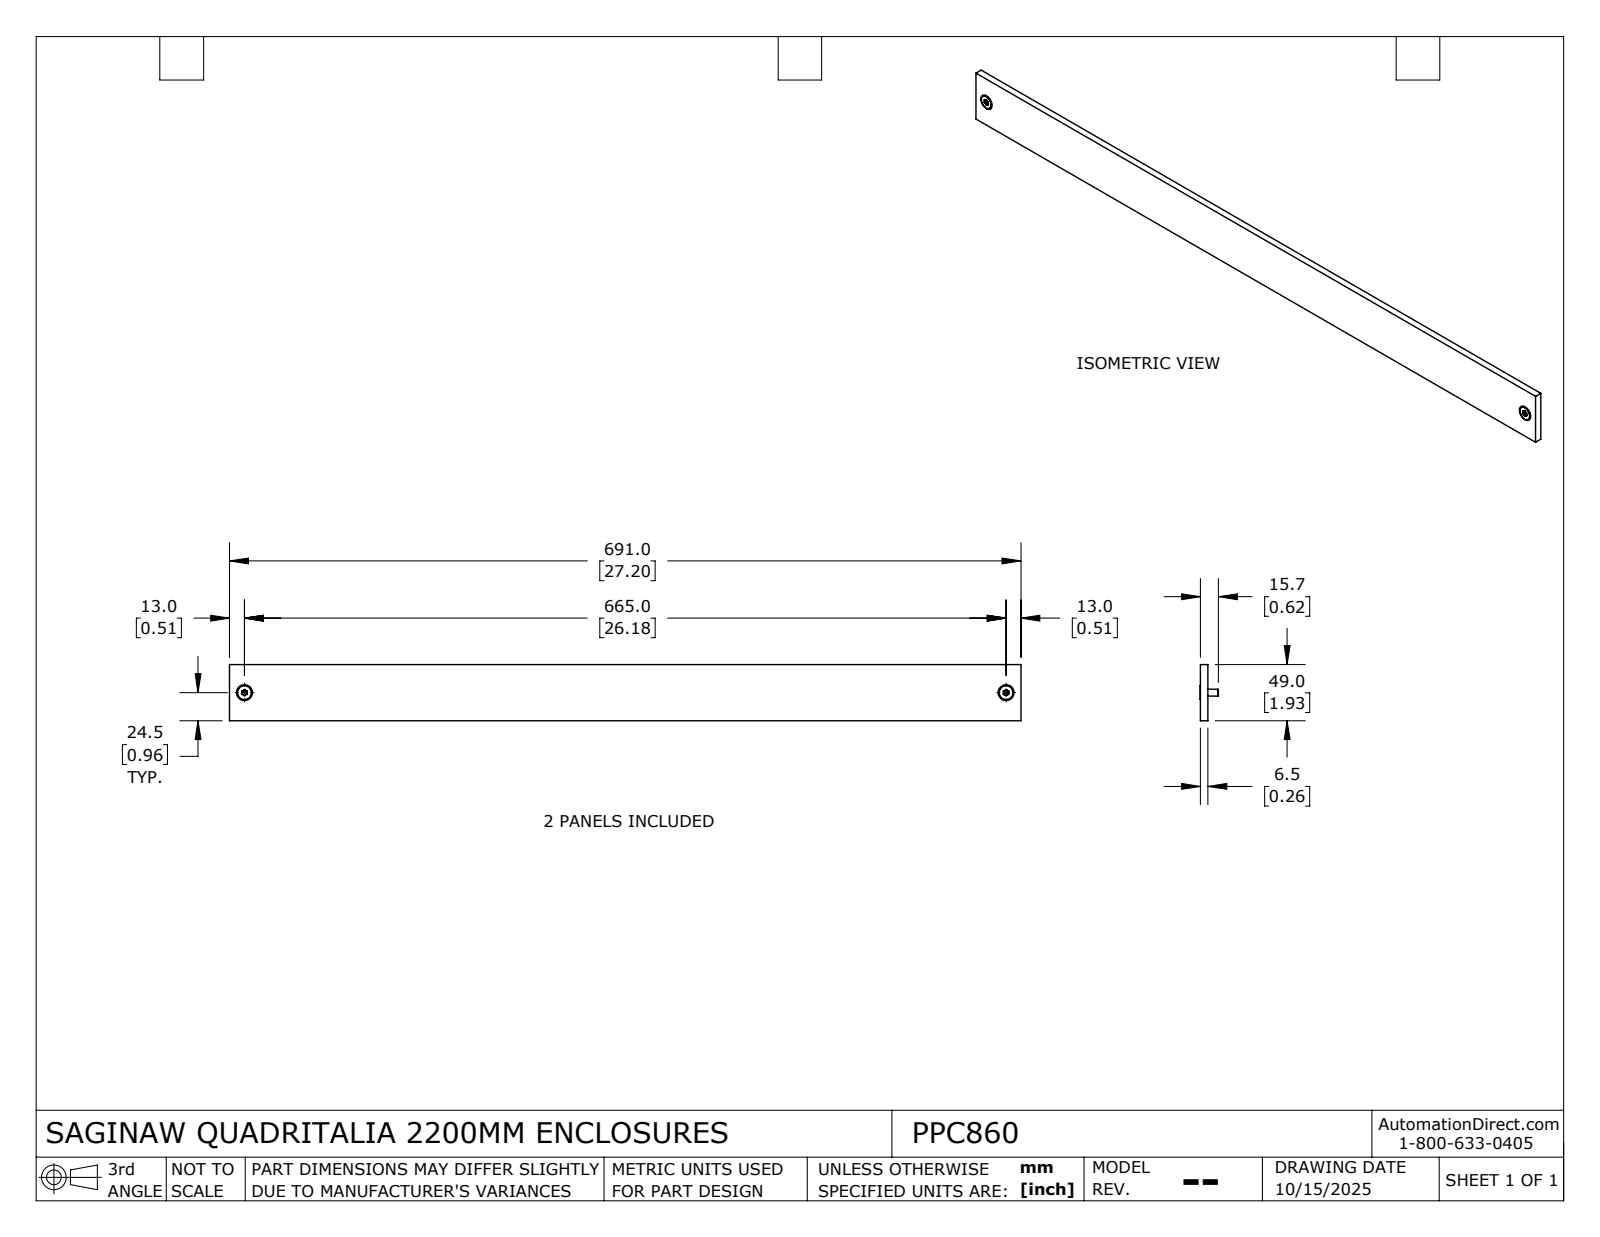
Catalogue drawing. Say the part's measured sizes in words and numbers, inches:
The part is named "PPC860". Its 3-D file was written by "SolidWorks 2024 (AUTOMOTIVE_DESIGN)". It is 2 solids with 182 faces: 86 planar, 68 cylindrical and 28 other. Overall it measures 74.764 by 27.205 by 0.63 inches. Its volume is 7.664 cubic inches and its surface area 264.8 square inches. Round holes: 4 of diameter 0.156. Round bosses or shafts: 4 of diameter 0.472, 4 of diameter 0.236. Partial cylindrical surfaces (rounded edges, fillets, slot ends): 48 of radius 0.02. The main face-to-face distances are 0.059, 72.835, 1.87, 1.929, 74.705, 72.776, 72.894, 1.811, 70.965, 74.764. The hole center spacings are 26.181, 72.835, 77.397.
